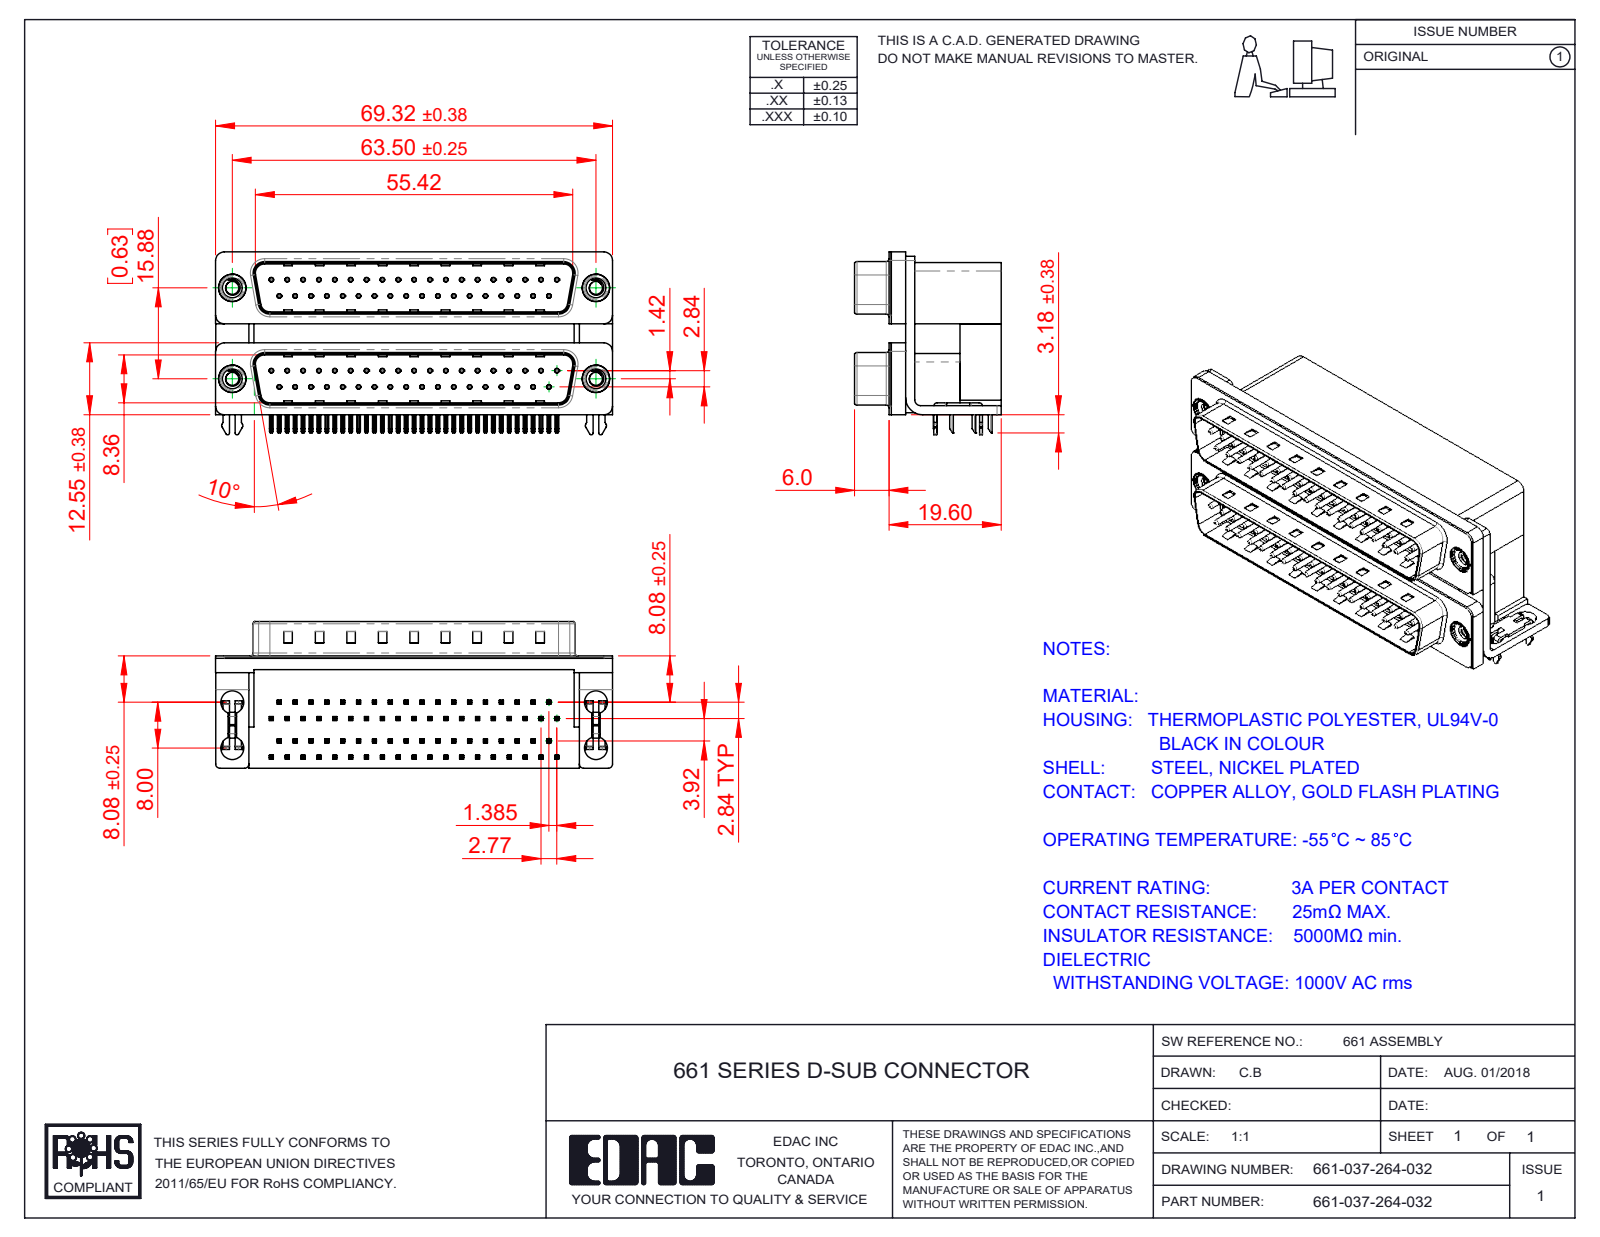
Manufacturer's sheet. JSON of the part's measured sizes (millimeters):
{"part_name": "661 Contact Bottom Lower; 661 Housing Upper_37 Contacts L; 661 Shell_37 Contacts; 661 Threaded Rivet_4-40 (+8 more)", "step_written_by": "SolidWorks 2020 (CONFIG_CONTROL_DESIGN)", "units": "millimeters", "bodies": {"solids": 87, "faces": 6734, "planar": 4352, "cylindrical": 1844, "other": 538}, "overall_size": [69.32, 31.93, 25.6], "volume_mm3": 27946, "surface_area_mm2": 28808, "round_holes": [[0.35, 74], [0.8, 74], [4, 8], [2.26, 4], [3.5, 4], [4.8, 4], [5, 4]], "round_bosses_or_shafts": [[0.75, 74], [4.9, 4], [4.75, 4], [3.9, 4]], "partial_cylinders_radius": [[0.25, 306], [0.12, 148], [0.5, 20], [1.5, 13], [0.75, 10], [0.9, 8], [1.6, 8], [2, 8]], "face_to_face_distances": [0.4, 19.2, 15.87, 7.2, 12, 10.7, 8.76, 15.52, 26.22, 2.19], "hole_center_spacings": [2.77, 5.54, 3.16, 8.31, 11.08, 13.85, 16.62, 19.39]}
